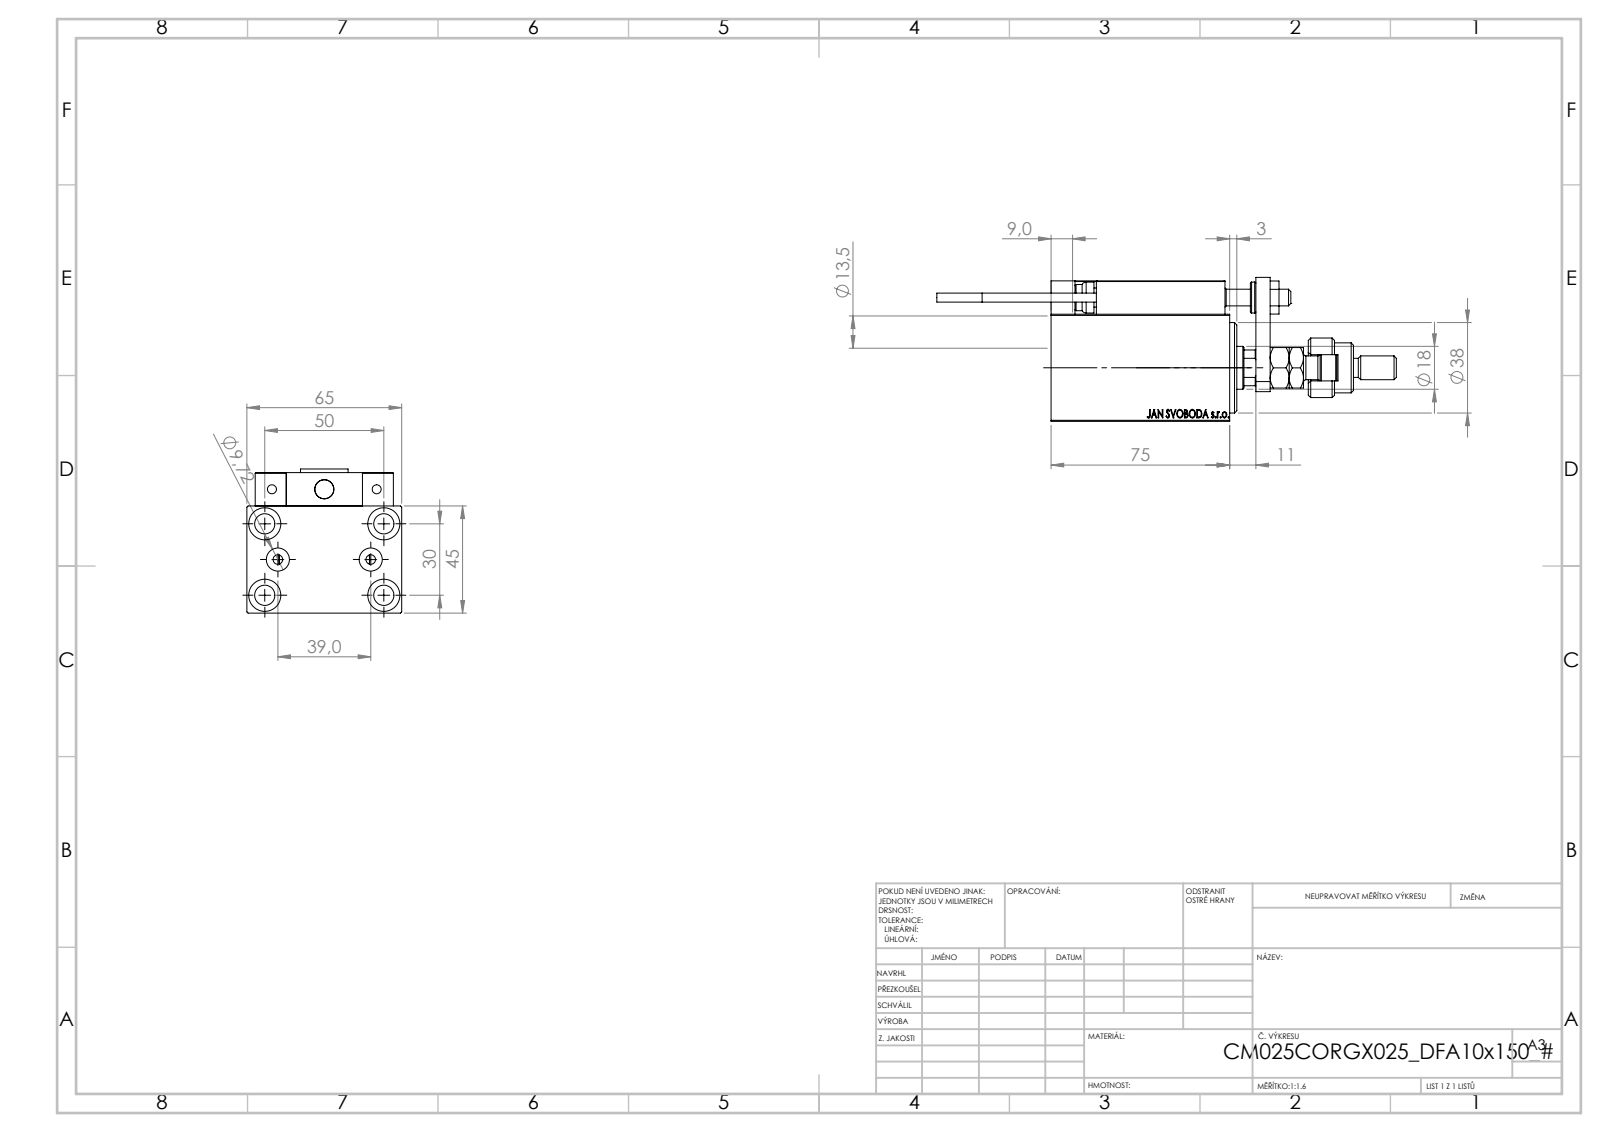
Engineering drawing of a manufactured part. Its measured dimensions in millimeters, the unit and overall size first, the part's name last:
Units: millimetres
Overall size (bounding box): 193 × 65 × 60.5
Round holes (diameter × count): ⌀4 ×6, ⌀8 ×5, ⌀8.5 ×5, ⌀3.2 ×4, ⌀13.5 ×4, ⌀5 ×2, ⌀9.72 ×2, ⌀7 ×1, ⌀14.5 ×1, ⌀18 ×1, ⌀21.5 ×1, ⌀27 ×1
Round bosses / shafts (diameter × count): ⌀5 ×2, ⌀3.8 ×2, ⌀25 ×1, ⌀21 ×1, ⌀16 ×1, ⌀13 ×1, ⌀11 ×1, ⌀10 ×1
Partial cylindrical surfaces — rounded edges, fillets, slot ends (radius × count): R0.3 ×30, R3 ×2, R5.5 ×1, R8.5 ×1, R8.75 ×1
Main face-to-face distances: 45, 65, 14, 6, 59, 3, 19, 64, 7, 13
Hole centre spacings: 15.98, 29.15, 46.96, 11.37, 19.5, 20, 27.07, 28.9
Volume: 248 219 mm³ · Surface area: 77 960 mm²
Bodies: 25 solids, 1363 faces (588 planar, 197 cylindrical, 578 other)
Part name (STEP PRODUCT): MFA; SWITCH_X_FRONT_BACK; V450CM_VC_B; X_Y_DFA (+7 more)
STEP written by: SolidWorks 2019 (CONFIG_CONTROL_DESIGN)
